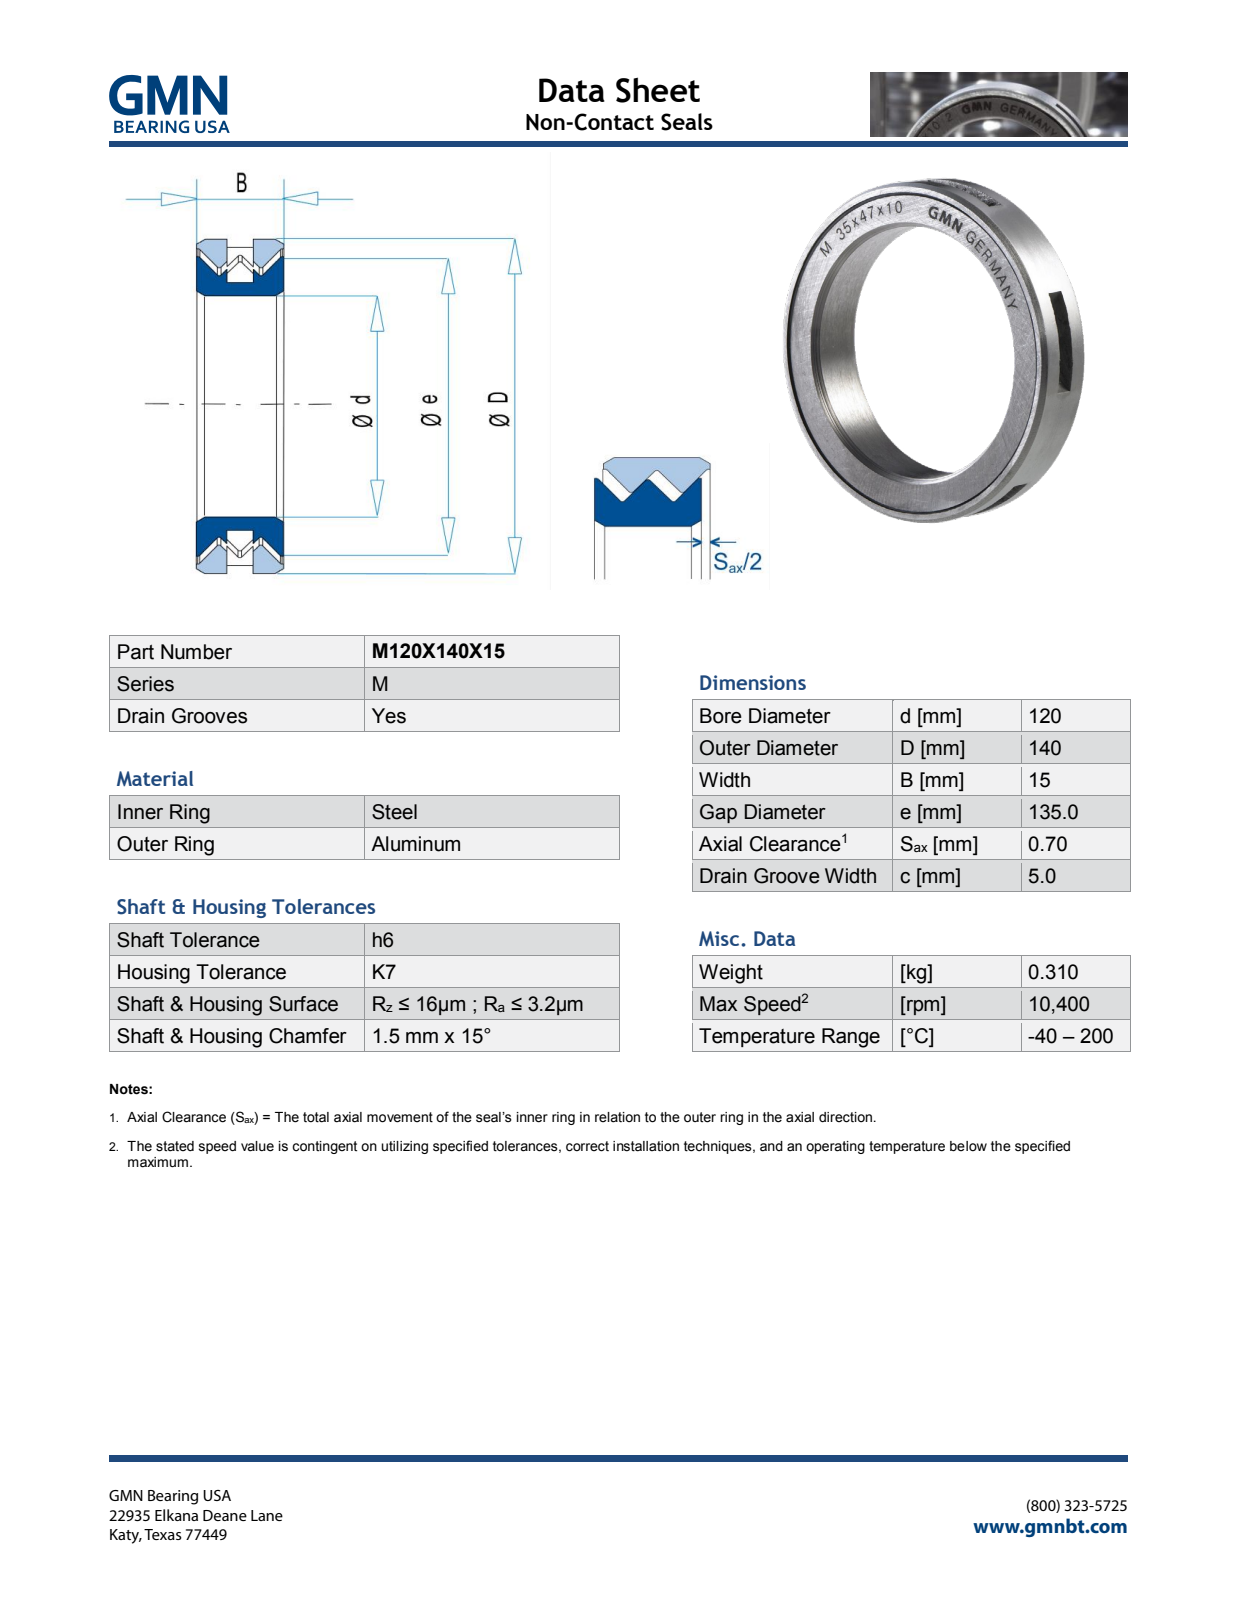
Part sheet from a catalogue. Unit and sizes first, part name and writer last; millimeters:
Units: millimetres
Overall size (bounding box): 140 × 140 × 15.07
Round holes (diameter × count): ⌀120 ×1, ⌀135.49 ×1
Round bosses / shafts (diameter × count): ⌀140 ×1, ⌀135 ×1
Partial cylindrical surfaces — rounded edges, fillets, slot ends (radius × count): R10 ×7
Main face-to-face distances: 15, 5, 10, 5.07, 10.07, 15.07, 0.54, 4.35, 0.55, 3.81
Volume: 55 321 mm³ · Surface area: 33 752 mm²
Bodies: 2 solids, 635 faces (548 planar, 33 cylindrical, 54 other)
Part name (STEP PRODUCT): M120X140X15_PRT
STEP written by: PRO/ENGINEER BY PARAMETRIC TECHNOLOGY CORPORATION, 2013150 (AUTOMOTIVE_DESIGN)
